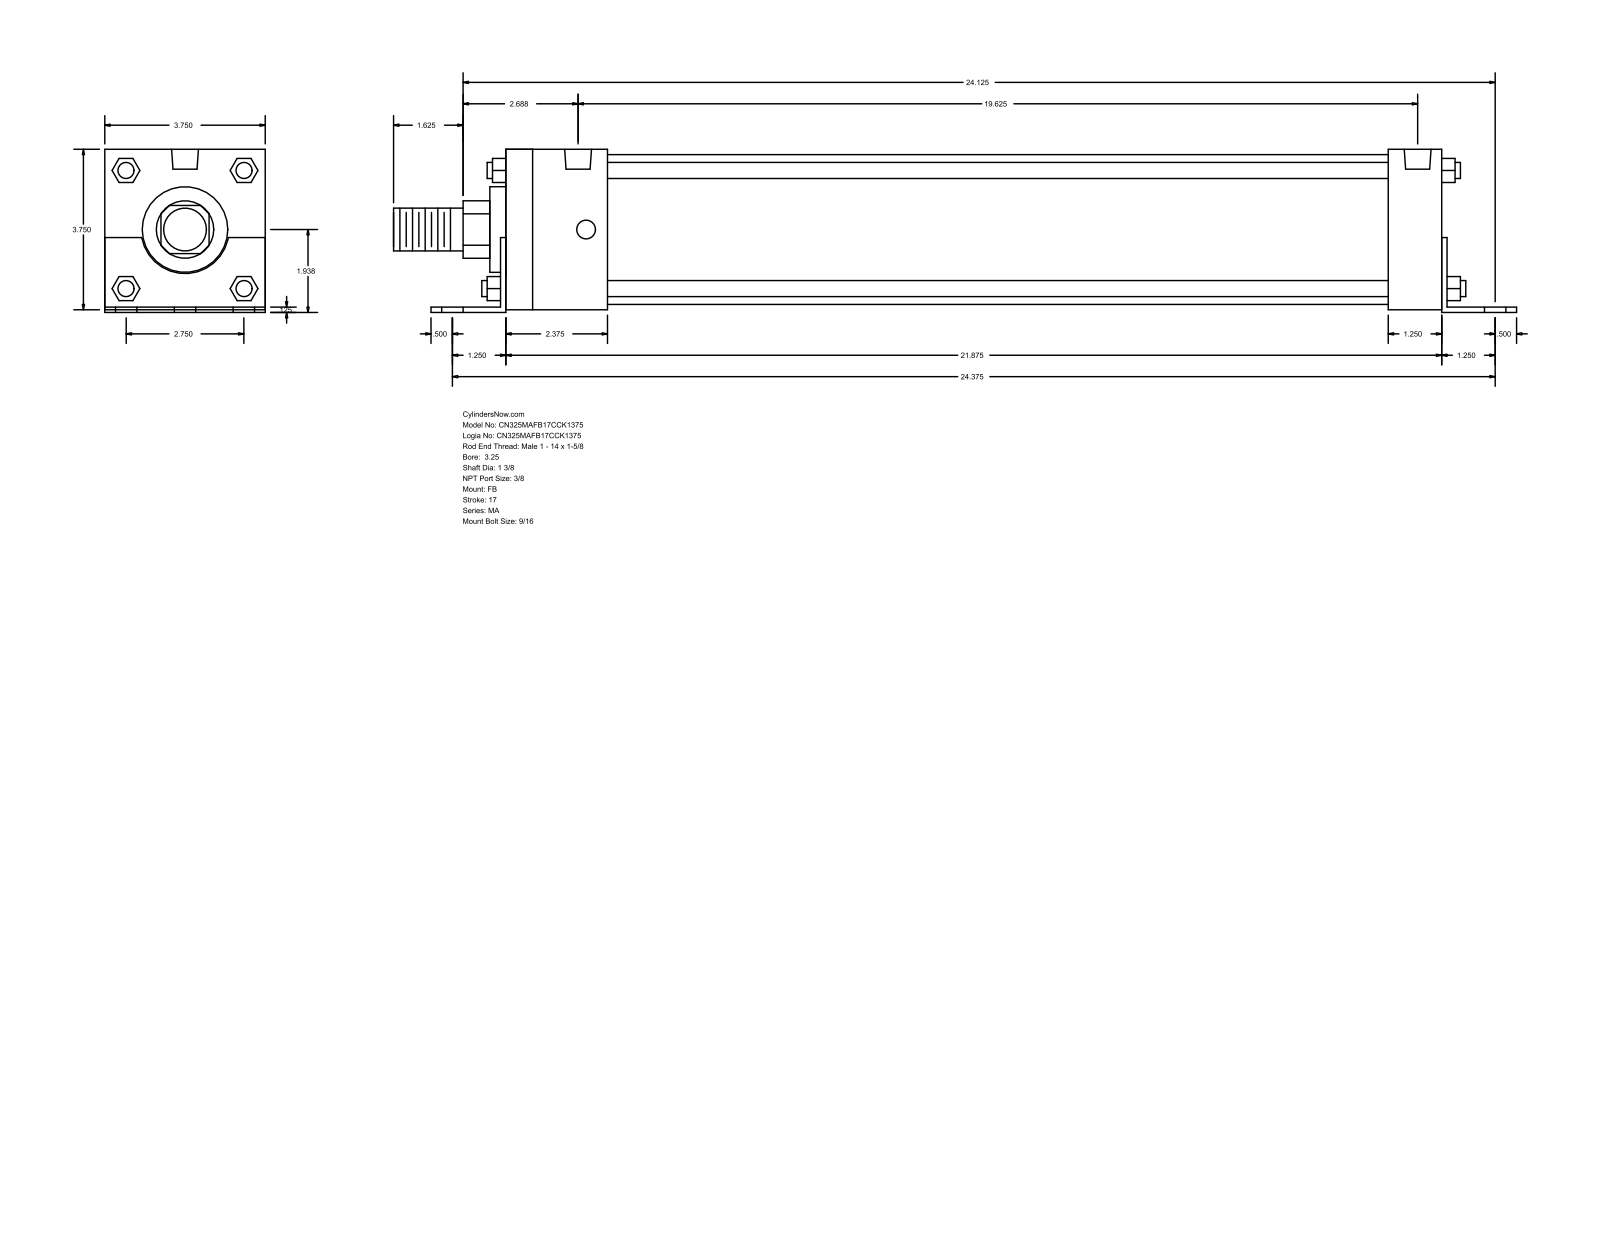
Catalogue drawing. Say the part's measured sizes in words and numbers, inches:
The part is named "MA_FB__0325_1.375". Its 3-D file was written by "GSSL Pune (CONFIG_CONTROL_DESIGN)". It is 0 solids with 140 faces: 105 planar, 35 cylindrical and 0 other. Overall it measures 26.25 by 3.813 by 3.75 inches. Round holes: 6 of diameter 0.563, 4 of diameter 0.437, 2 of diameter 0.627. Round bosses or shafts: 4 of diameter 0.375, 1 of diameter 3.5, 1 of diameter 2, 1 of diameter 1.375, 1 of diameter 1. Partial cylindrical surfaces (rounded edges, fillets, slot ends): 1 of radius 0.672, 1 of radius 1.03. The main face-to-face distances are 3.75, 0.125, 0.063, 3.812, 0.062, 3.687, 0.125, 21.875, 22, 1.25. The hole center spacings are 1.375, 24.413, 24.375, 2.275, 2.427, 2.75, 3.243, 3.414.
